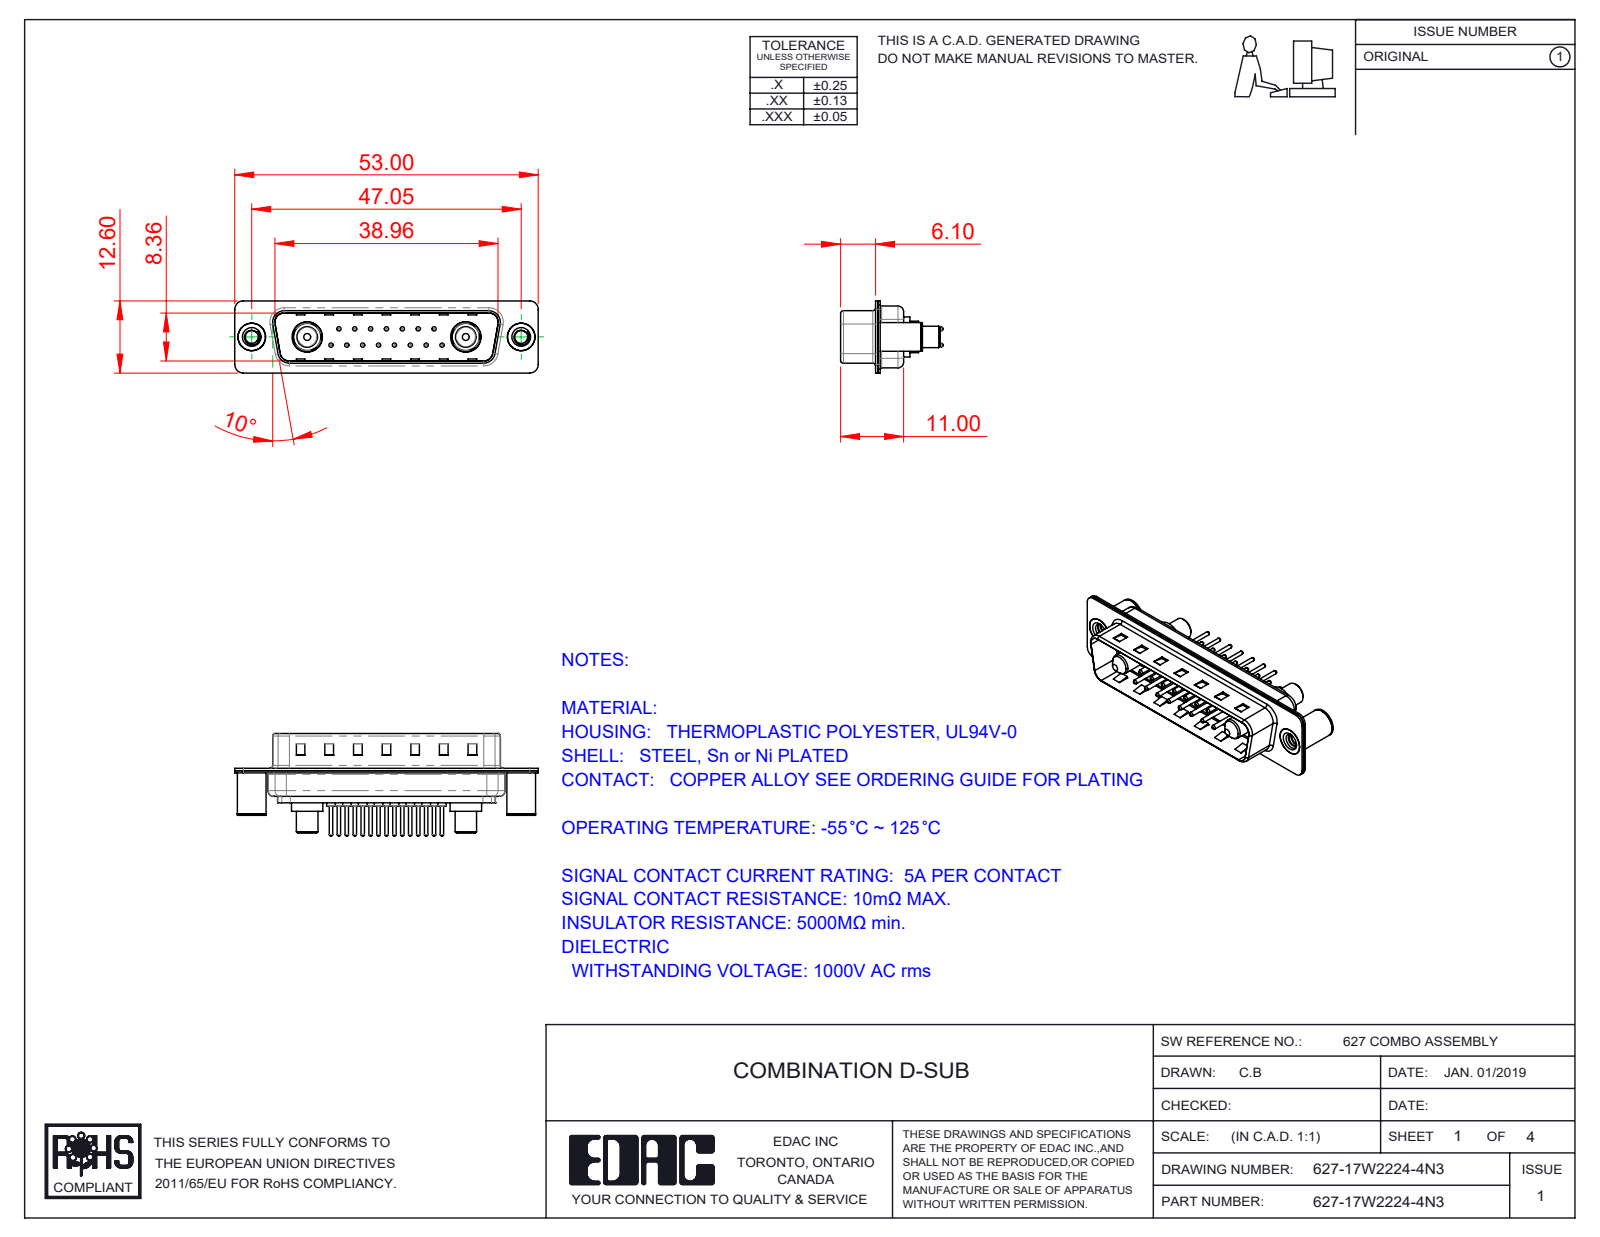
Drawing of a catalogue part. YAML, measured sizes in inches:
part_name: "627Combo Contact Row 2_24; 627Combo Threaded Board Spacer_3; 627-17W2224-4N3; 627Combo Shell Front_25 Contacts (+4 more)"
step_written_by: "SolidWorks 2016 (CONFIG_CONTROL_DESIGN)"
units: inches
bodies: {solids: 24, faces: 1045, planar: 296, cylindrical: 409, other: 340}
overall_size: [2.087, 0.705, 0.496]
volume: 0.184
surface_area: 10.96
round_holes:
  - {diameter: 0.03, count: 15}
  - {diameter: 0.063, count: 15}
  - {diameter: 0.079, count: 15}
  - {diameter: 0.089, count: 2}
  - {diameter: 0.128, count: 2}
  - {diameter: 0.157, count: 2}
  - {diameter: 0.189, count: 2}
  - {diameter: 0.191, count: 2}
  - {diameter: 0.209, count: 2}
round_bosses_or_shafts:
  - {diameter: 0.059, count: 15}
  - {diameter: 0.024, count: 15}
  - {diameter: 0.217, count: 2}
  - {diameter: 0.205, count: 2}
  - {diameter: 0.197, count: 2}
  - {diameter: 0.193, count: 2}
  - {diameter: 0.187, count: 2}
  - {diameter: 0.148, count: 2}
partial_cylinders:
  - {radius: 0.059, count: 16}
  - {radius: 0.079, count: 12}
  - {radius: 0.02, count: 8}
  - {radius: 0.063, count: 8}
  - {radius: 0.01, count: 4}
  - {radius: 0.024, count: 4}
  - {radius: 0.026, count: 4}
  - {radius: 0.035, count: 4}
face_to_face_distances: [0.016, 0.032, 0.377, 0.345, 0.059, 0.22, 0.205, 0.031, 0.048, 0.393]
hole_center_spacings: [0.124, 0.109, 0.218, 0.327, 0.198, 0.295, 0.436, 0.198]
